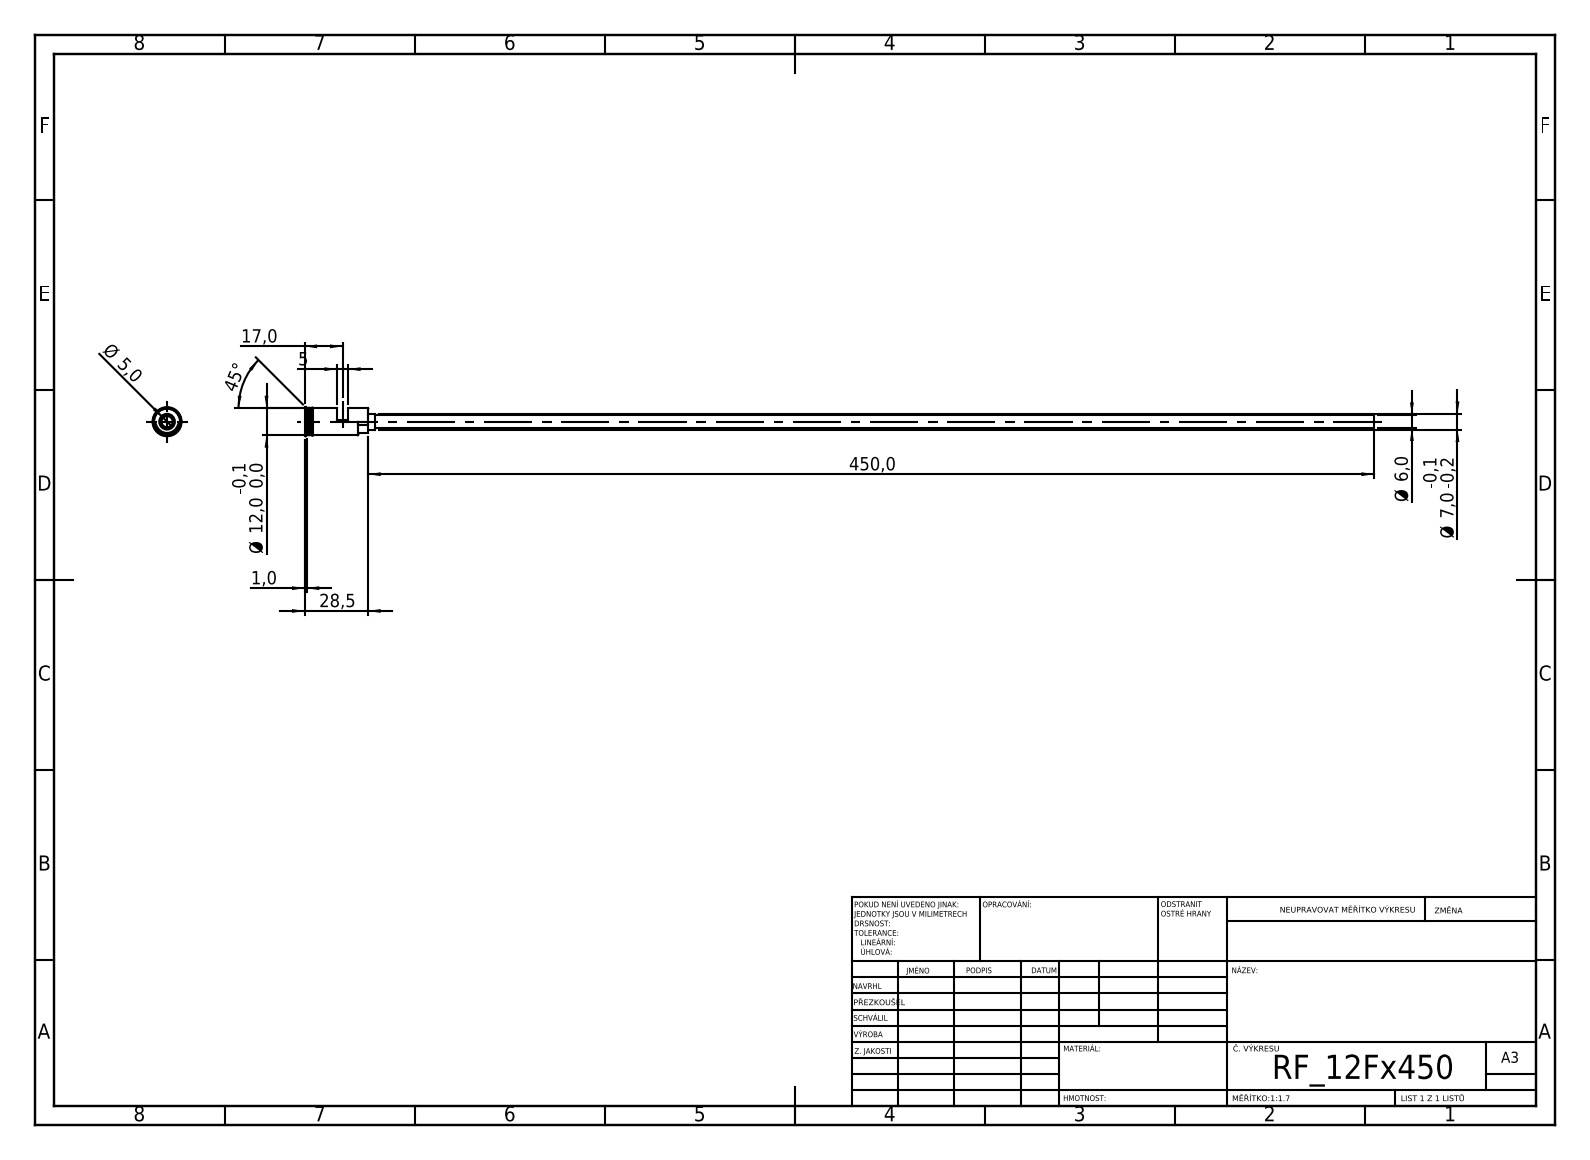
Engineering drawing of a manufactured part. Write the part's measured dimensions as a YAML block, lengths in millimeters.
step_written_by: "SolidWorks 2019 (CONFIG_CONTROL_DESIGN)"
units: millimeters
bodies: {solids: 1, faces: 55, planar: 24, cylindrical: 19, other: 12}
overall_size: [478.5, 13, 13]
volume: 6491
surface_area: 17169
round_holes:
  - {diameter: 5, count: 1}
round_bosses_or_shafts:
  - {diameter: 13, count: 1}
  - {diameter: 12, count: 1}
  - {diameter: 11.8, count: 1}
  - {diameter: 7, count: 1}
  - {diameter: 6, count: 1}
partial_cylinders:
  - {radius: 3, count: 2}
  - {radius: 5.05, count: 1}
face_to_face_distances: [14.5, 12.5, 2, 14, 26.5, 28.5, 9, 5, 17.5, 19.5]
